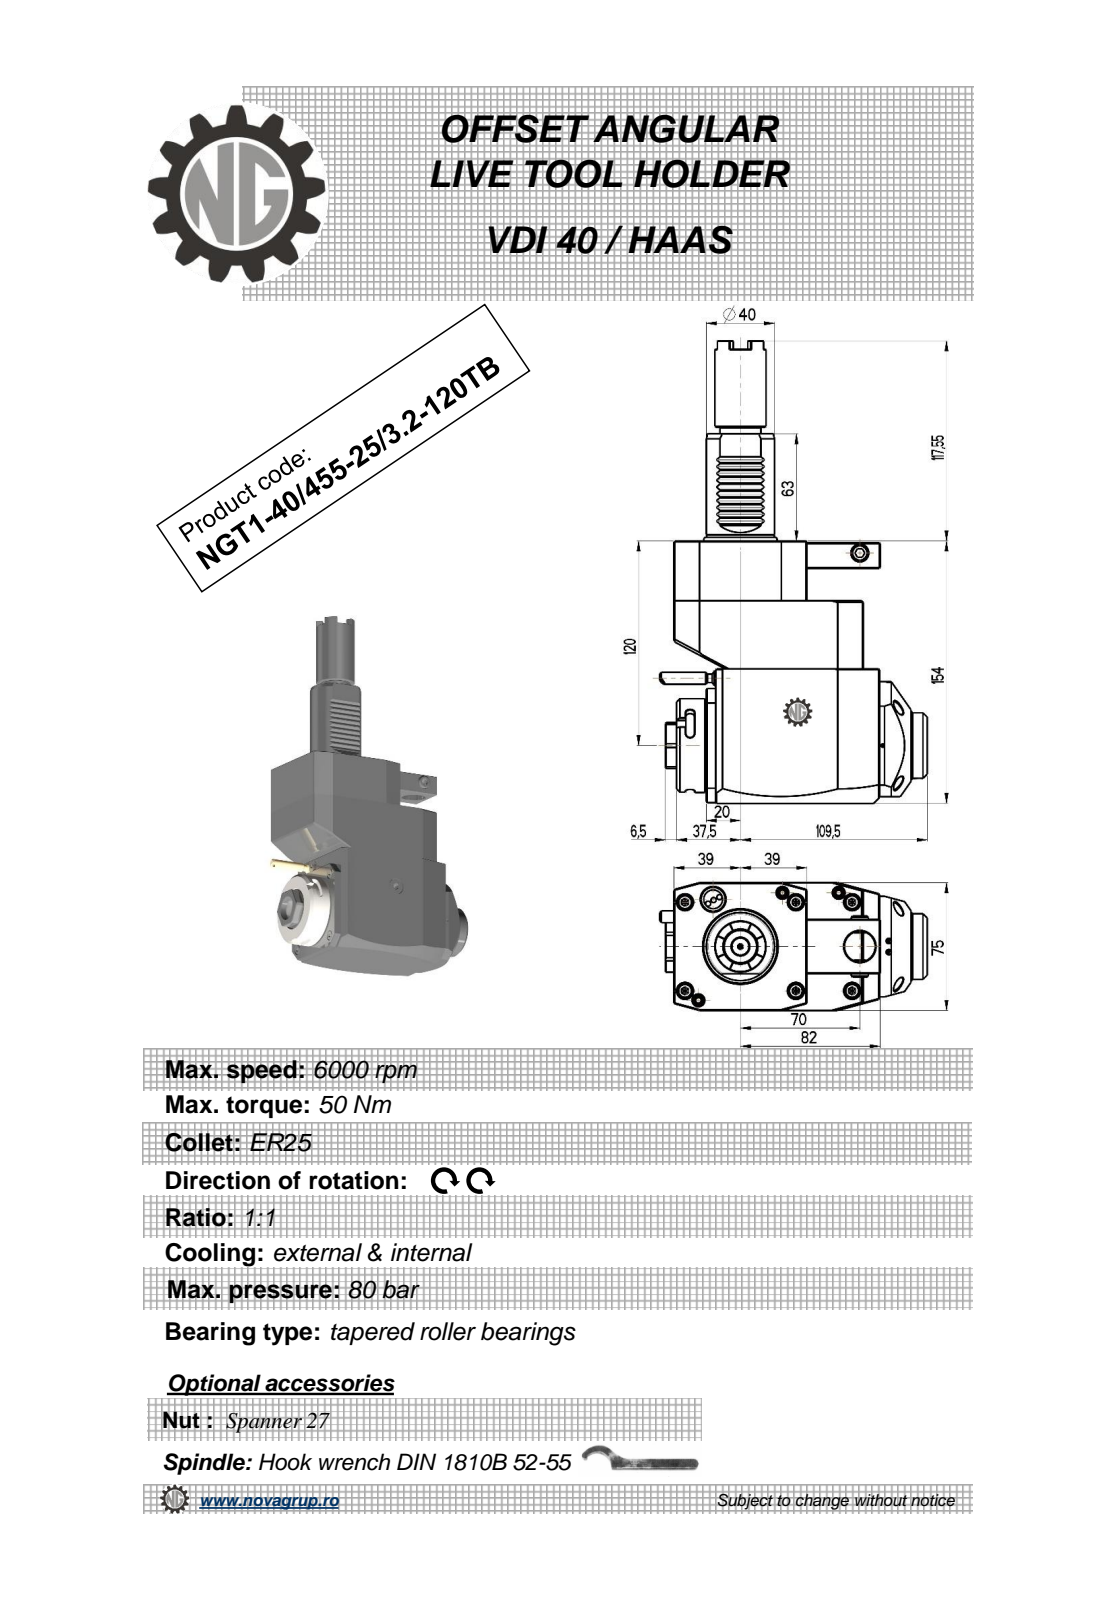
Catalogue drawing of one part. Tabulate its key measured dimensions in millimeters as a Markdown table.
| quantity | value |
| --- | --- |
| part name | NGT1_40_455_25_3_2_120TB |
| STEP written by | PRO/ENGINEER BY PARAMETRIC TECHNOLOGY CORPORATION, 2010280 (CONFIG_CONTROL_DESIGN) |
| units | millimeters |
| bodies | 1 solid, 380 faces (216 planar, 78 cylindrical, 86 other) |
| overall size | 271.55 × 156.83 × 75 |
| volume | 1 320 000 mm³ |
| surface area | 96 142 mm² |
| round holes (diameter × count) | 18 × 2, 2.5 × 1, 3 × 1, 9.5 × 1, 20 × 1 |
| round bosses / shafts (diameter × count) | 8.96 × 2, 55 × 1, 48 × 1, 40 × 1, 38.5 × 1, 30 × 1, 24 × 1, 10 × 1 |
| partial cylindrical surfaces (radius × count) | 0.3 × 10, 2.5 × 6, 180 × 2, 0.5 × 1, 4.25 × 1, 15 × 1, 24.5 × 1, 37.5 × 1 |
| main face-to-face distances | 75, 154, 19, 119, 59, 111, 92, 35, 17.5, 53.5 |
| hole center spacings | 43.2, 70, 75.07, 112.5 |
